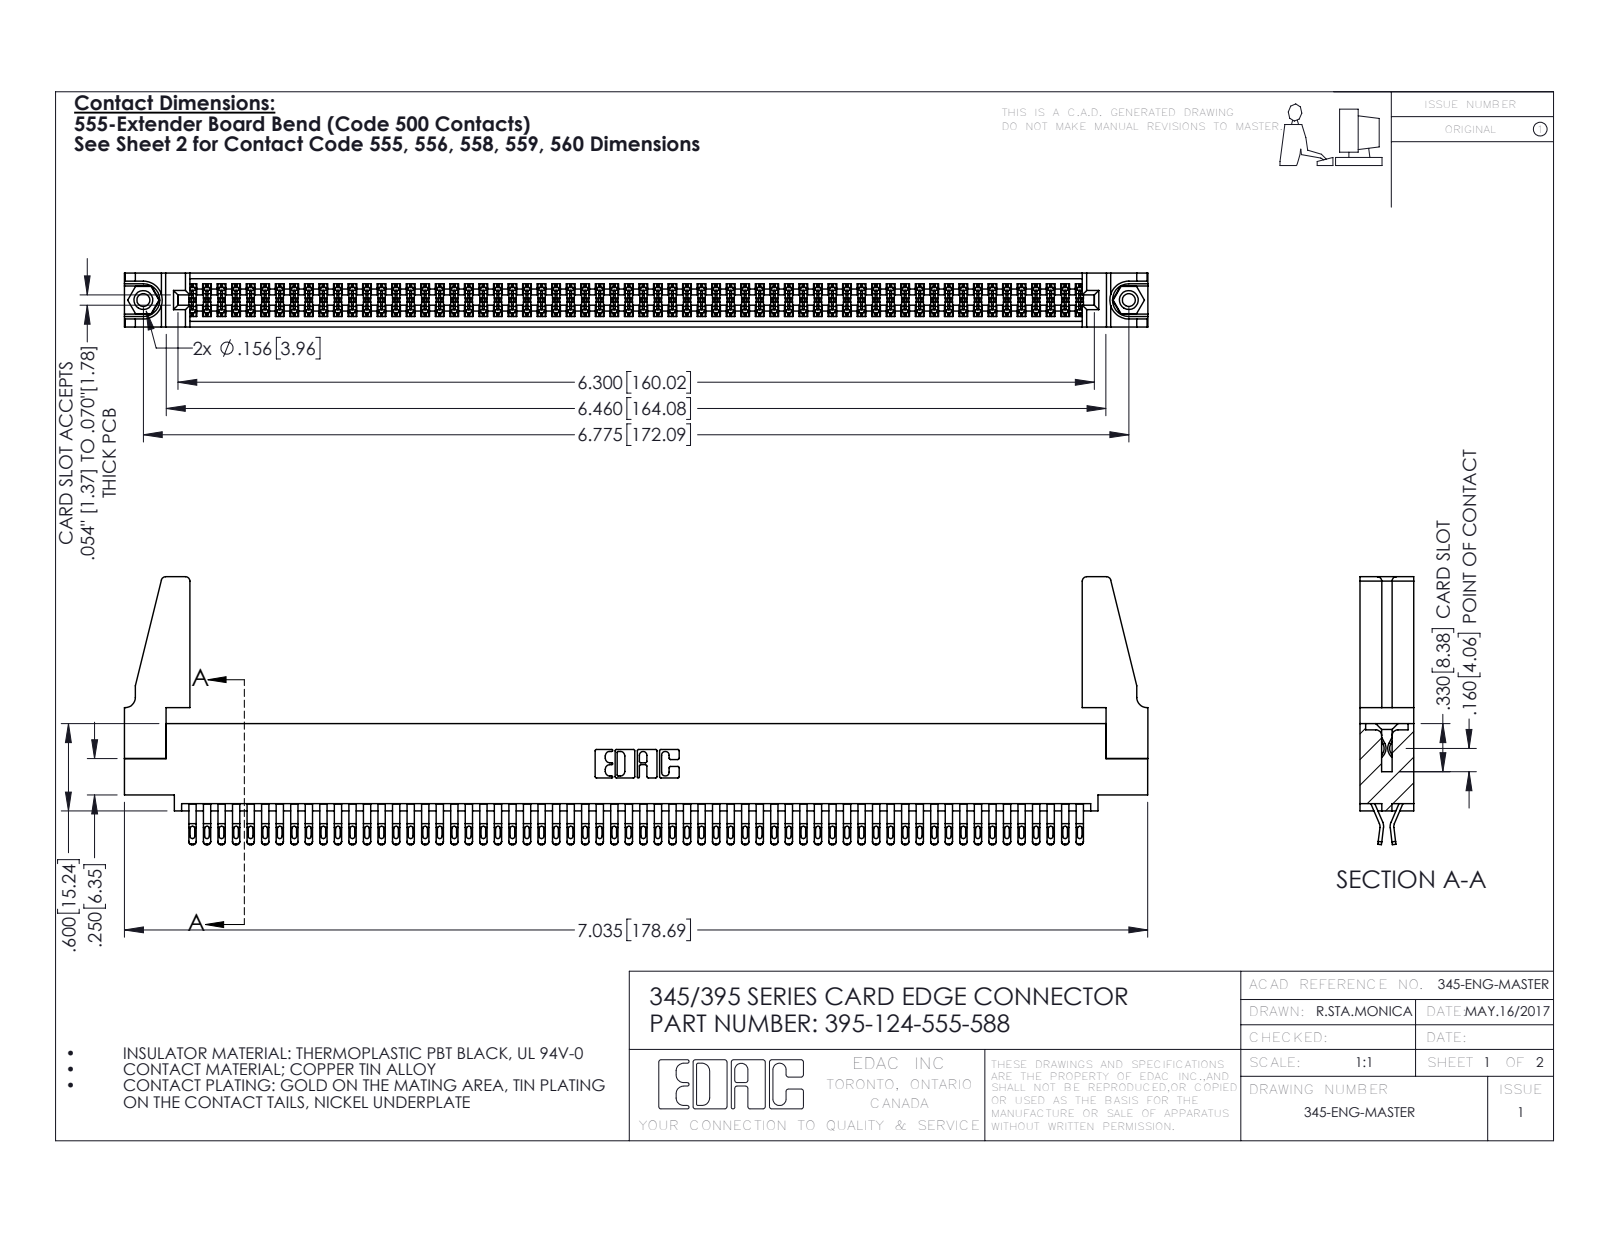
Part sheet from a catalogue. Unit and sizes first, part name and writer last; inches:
Units: inches
Overall size (bounding box): 7.036 × 1.842 × 0.37
Round holes (diameter × count): ⌀0.089 ×2, ⌀0.125 ×2, ⌀0.156 ×2, ⌀0.064 ×1
Round bosses / shafts (diameter × count): ⌀0.155 ×2
Partial cylindrical surfaces — rounded edges, fillets, slot ends (radius × count): R0.016 ×310, R0.02 ×248, R0.006 ×186, R0.01 ×22, R0.03 ×8, R0.007 ×6, R0.031 ×6, R0.026 ×3
Main face-to-face distances: 0.072, 0.298, 0.37, 0.025, 0.2, 0.098, 0.272, 0.225, 0.175, 0.149
Hole centre spacings: 0.27, 6.539, 6.775
Volume: 1.287 in³ · Surface area: 48.38 in²
Bodies: 129 solids, 7198 faces (4000 planar, 3182 cylindrical, 16 other)
Part name (STEP PRODUCT): 345-220-078_345-220-088; 345-292-001_555 Tail; 345 Part_0.110 Offset - 0.156 Dia-TH; 345-250-001_345-250-001-102 (+1 more)
STEP written by: SolidWorks 2016 (CONFIG_CONTROL_DESIGN)
